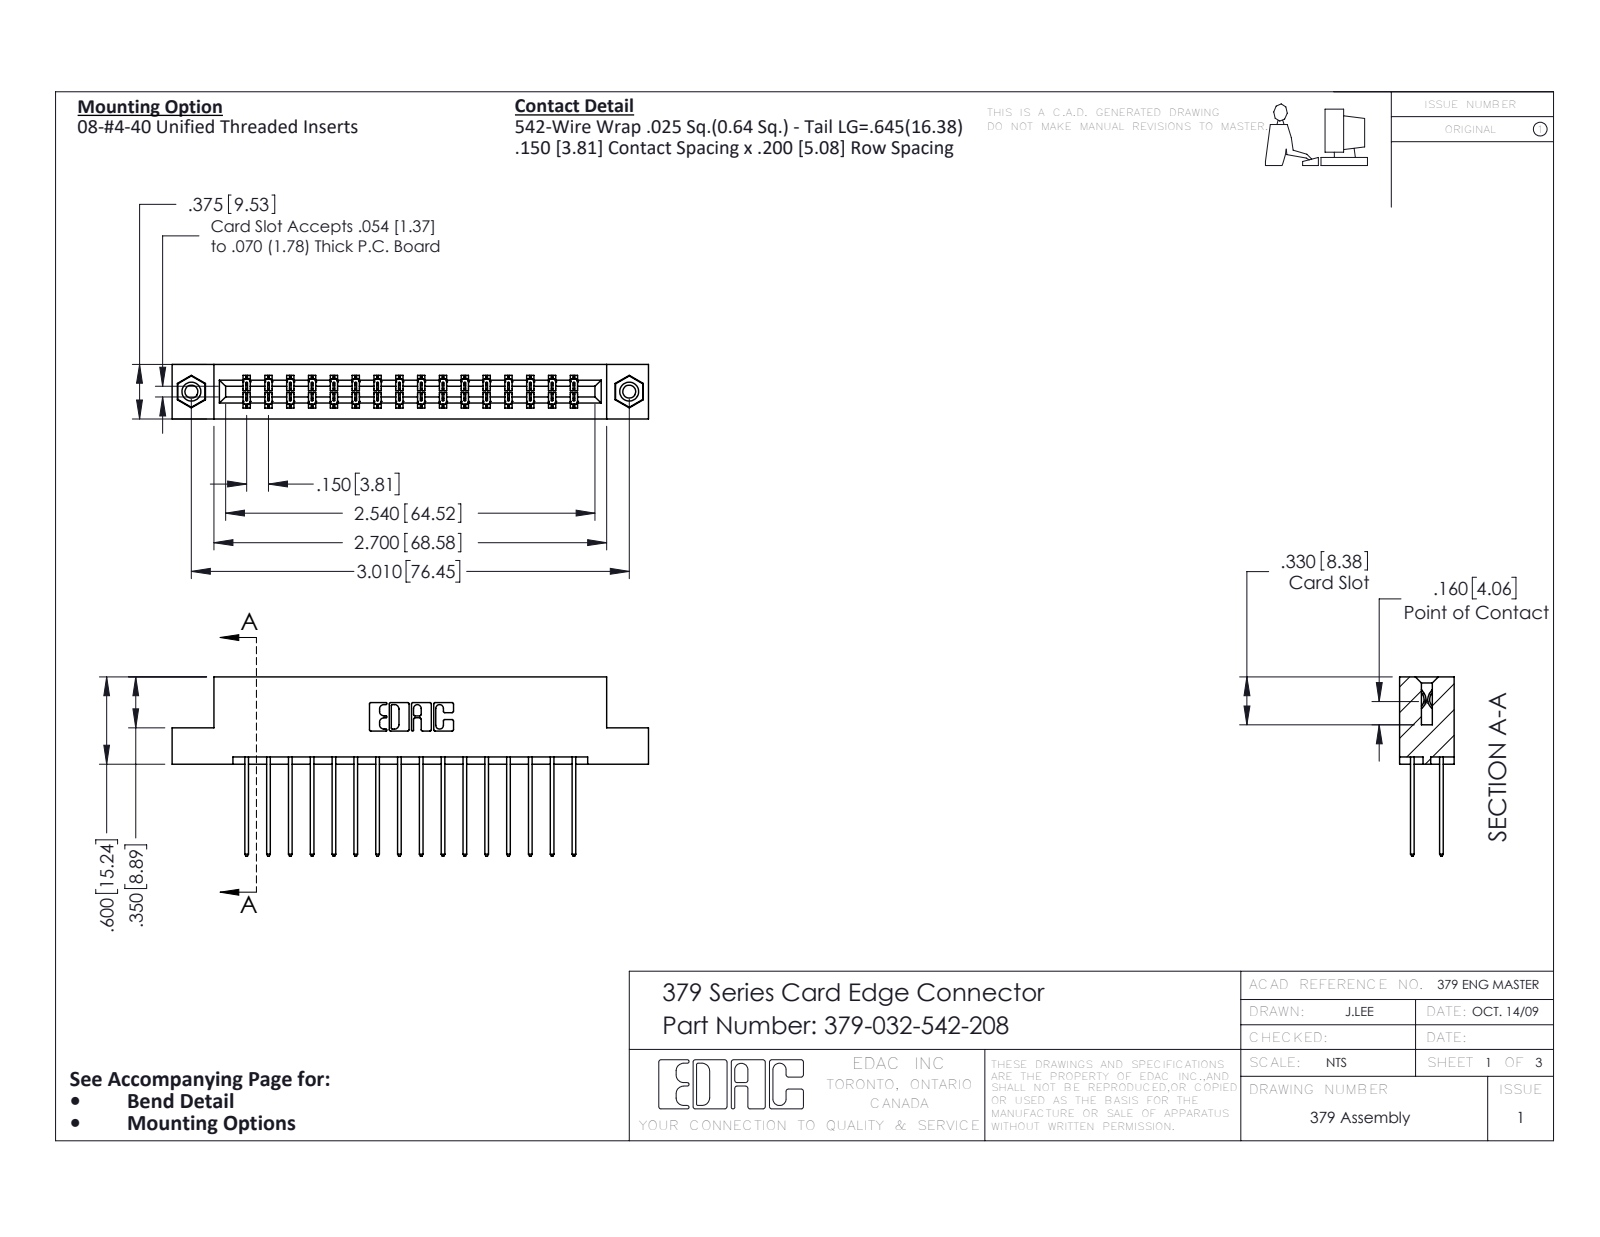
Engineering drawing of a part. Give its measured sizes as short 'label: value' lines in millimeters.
name: 345-250-001_345-250-003-102; 379 Part_Flush - .156 Dia - TI; 345-292-001_345-293-142; 379-032-542-208
written by: SolidWorks 2020 (CONFIG_CONTROL_DESIGN)
unit: mm
bodies: 35 solids, 1838 faces (1254 planar, 568 cylindrical, 16 other)
size: 83.2 × 31.3 × 9.5
volume: 8 690 mm³; area: 10 280 mm²
holes: 2× ⌀2.3, 2× ⌀3.2, 2× ⌀4
bosses: 2× ⌀3.9
rounds: 63× R0.2, 32× R0.3, 22× R0.3, 6× R0.2, 6× R0.8, 3× R0.7, 2× R0.4, 2× R0.6
face distances: 7.6, 1.9, 5.1, 2.5, 9.5, 7, 3.8, 1.3, 15.2, 0.6
hole spacings: 76.5
